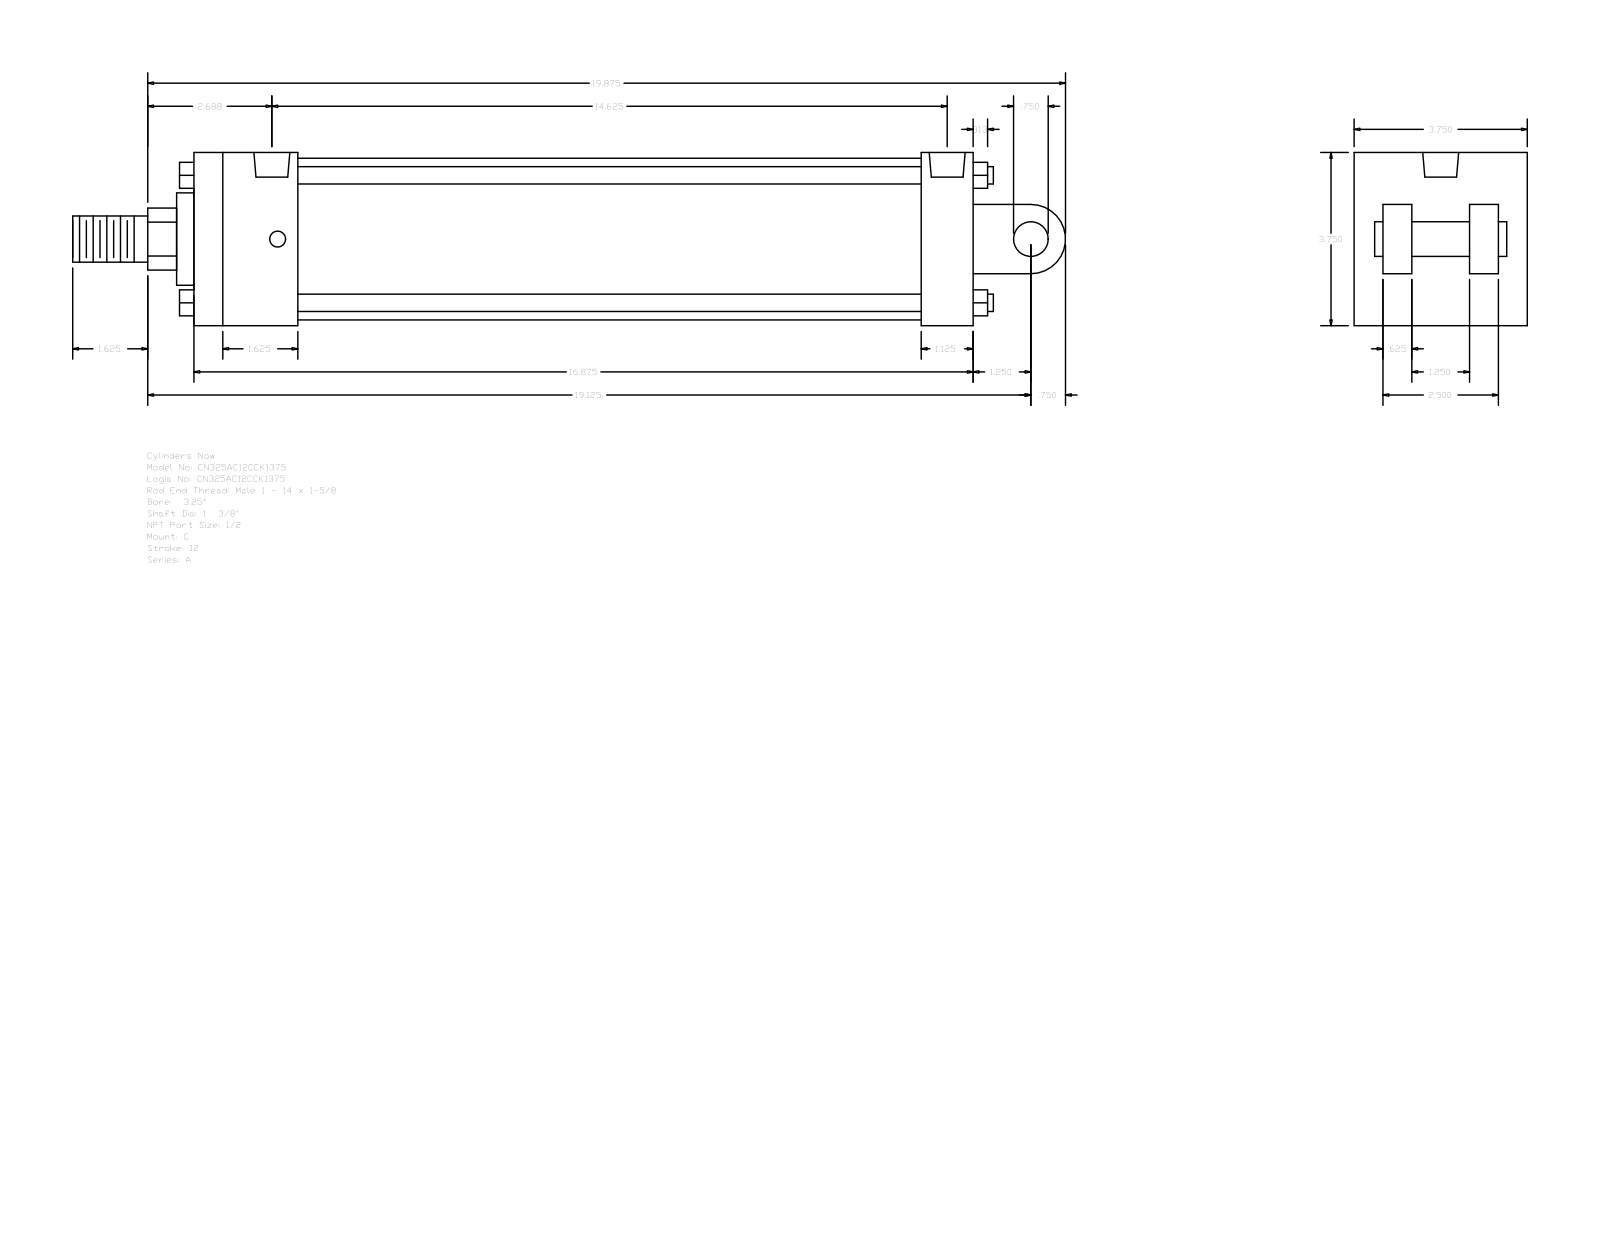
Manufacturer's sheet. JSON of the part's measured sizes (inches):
{"part_name": "A_C__0325_1.375", "step_written_by": "GSSL Pune (CONFIG_CONTROL_DESIGN)", "units": "inches", "bodies": {"solids": 0, "faces": 135, "planar": 102, "cylindrical": 33, "other": 0}, "overall_size": [21.5, 3.75, 3.75], "round_holes": [[0.344, 4], [0.778, 2]], "round_bosses_or_shafts": [[0.375, 4], [3.5, 1], [2, 1], [1.375, 1], [1, 1], [0.75, 1]], "partial_cylinders_radius": [[0.672, 1], [0.75, 1]], "face_to_face_distances": [3.75, 16.875, 0.625, 1.125, 2.5, 2.625, 2.25, 3.125, 1.25, 1.875], "hole_center_spacings": [0.125, 14.375, 14.5, 14.625]}
